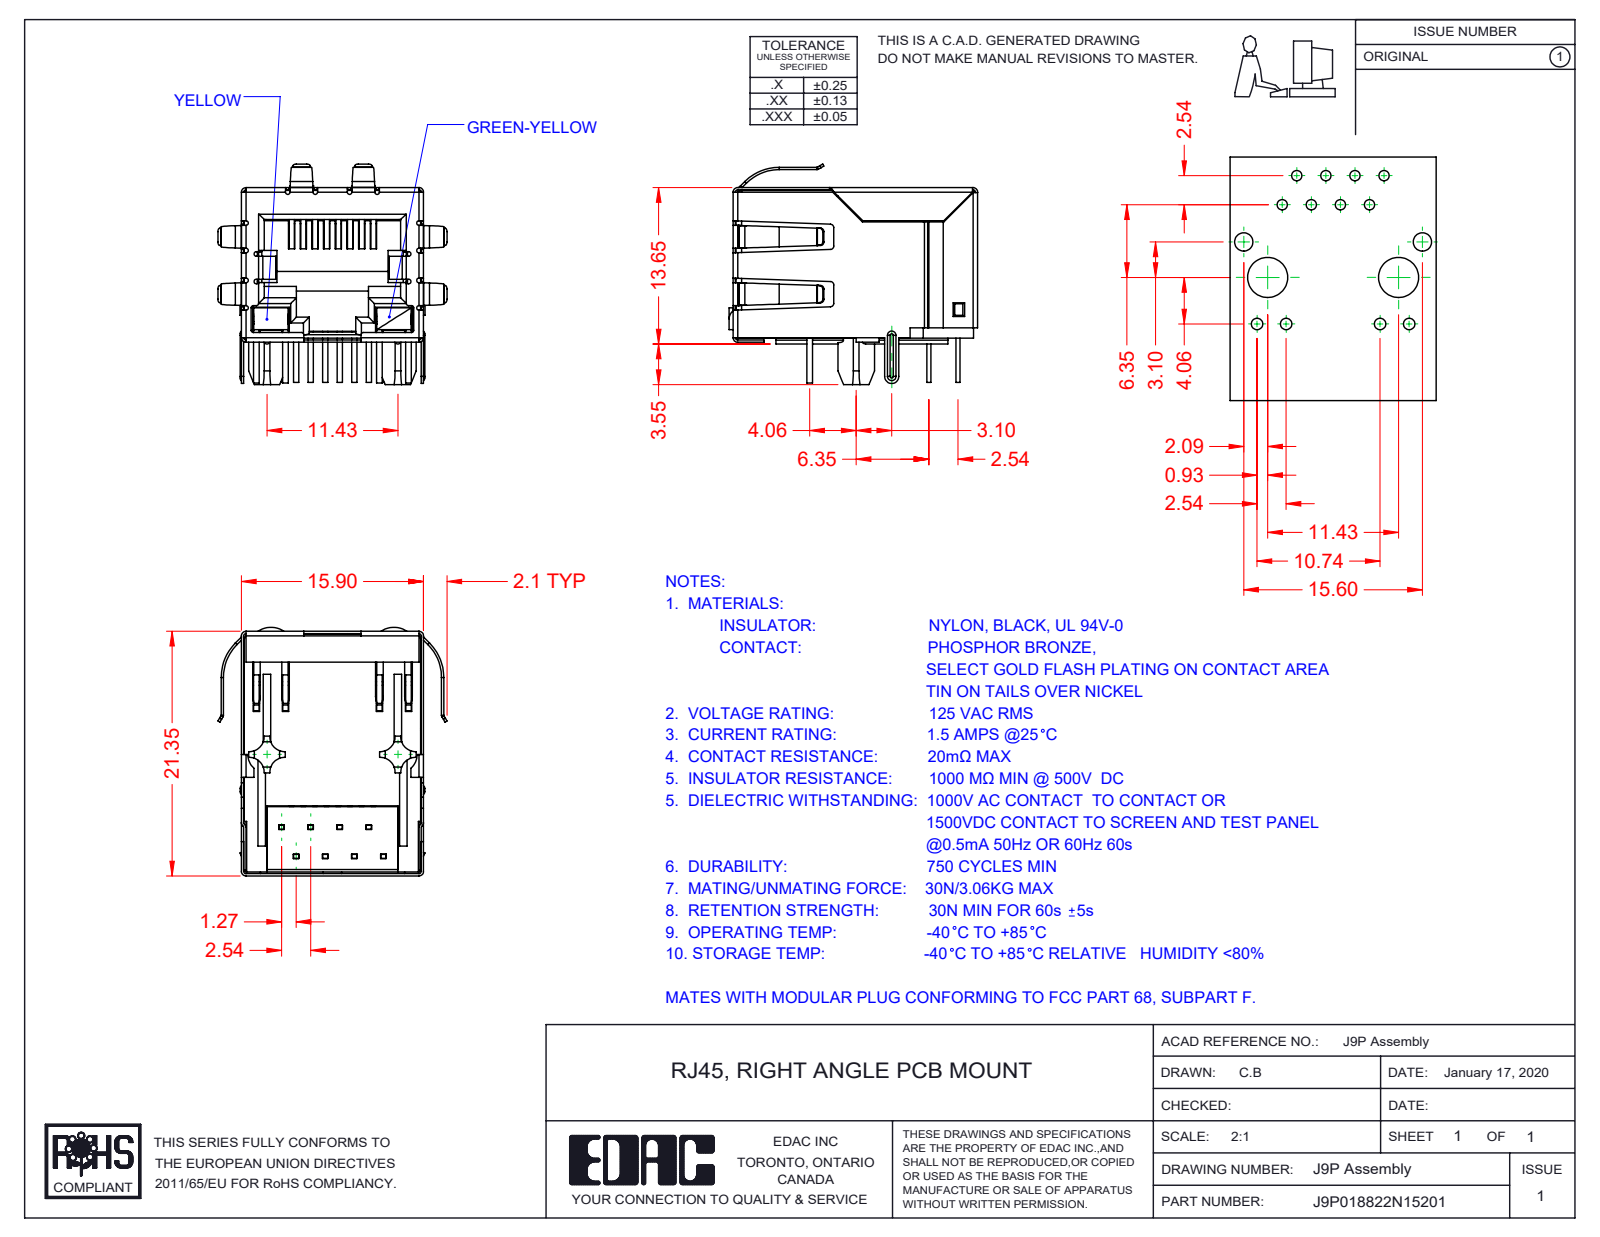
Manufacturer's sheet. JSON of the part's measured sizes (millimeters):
{"part_name": "9P-LED Contact Lock; 9P-LED LED LH_1-Yellow; 9P-LED LED RH_5-Green-Yellow; 9P-LED Contacts (+4 more)", "step_written_by": "SolidWorks 2016 (CONFIG_CONTROL_DESIGN)", "units": "millimeters", "bodies": {"solids": 13, "faces": 1474, "planar": 1042, "cylindrical": 338, "other": 94}, "overall_size": [21.7, 20, 19.25], "volume_mm3": 2687, "surface_area_mm2": 7515, "partial_cylinders_radius": [[0.2, 39], [0.5, 22], [0.3, 20], [0.4, 16], [1.3, 8], [0.23, 5], [0.11, 4], [0.31, 4]], "face_to_face_distances": [15.45, 15.7, 15.65, 0.35, 0.54, 15.5, 12.36, 0.6, 1.4, 0.59]}
